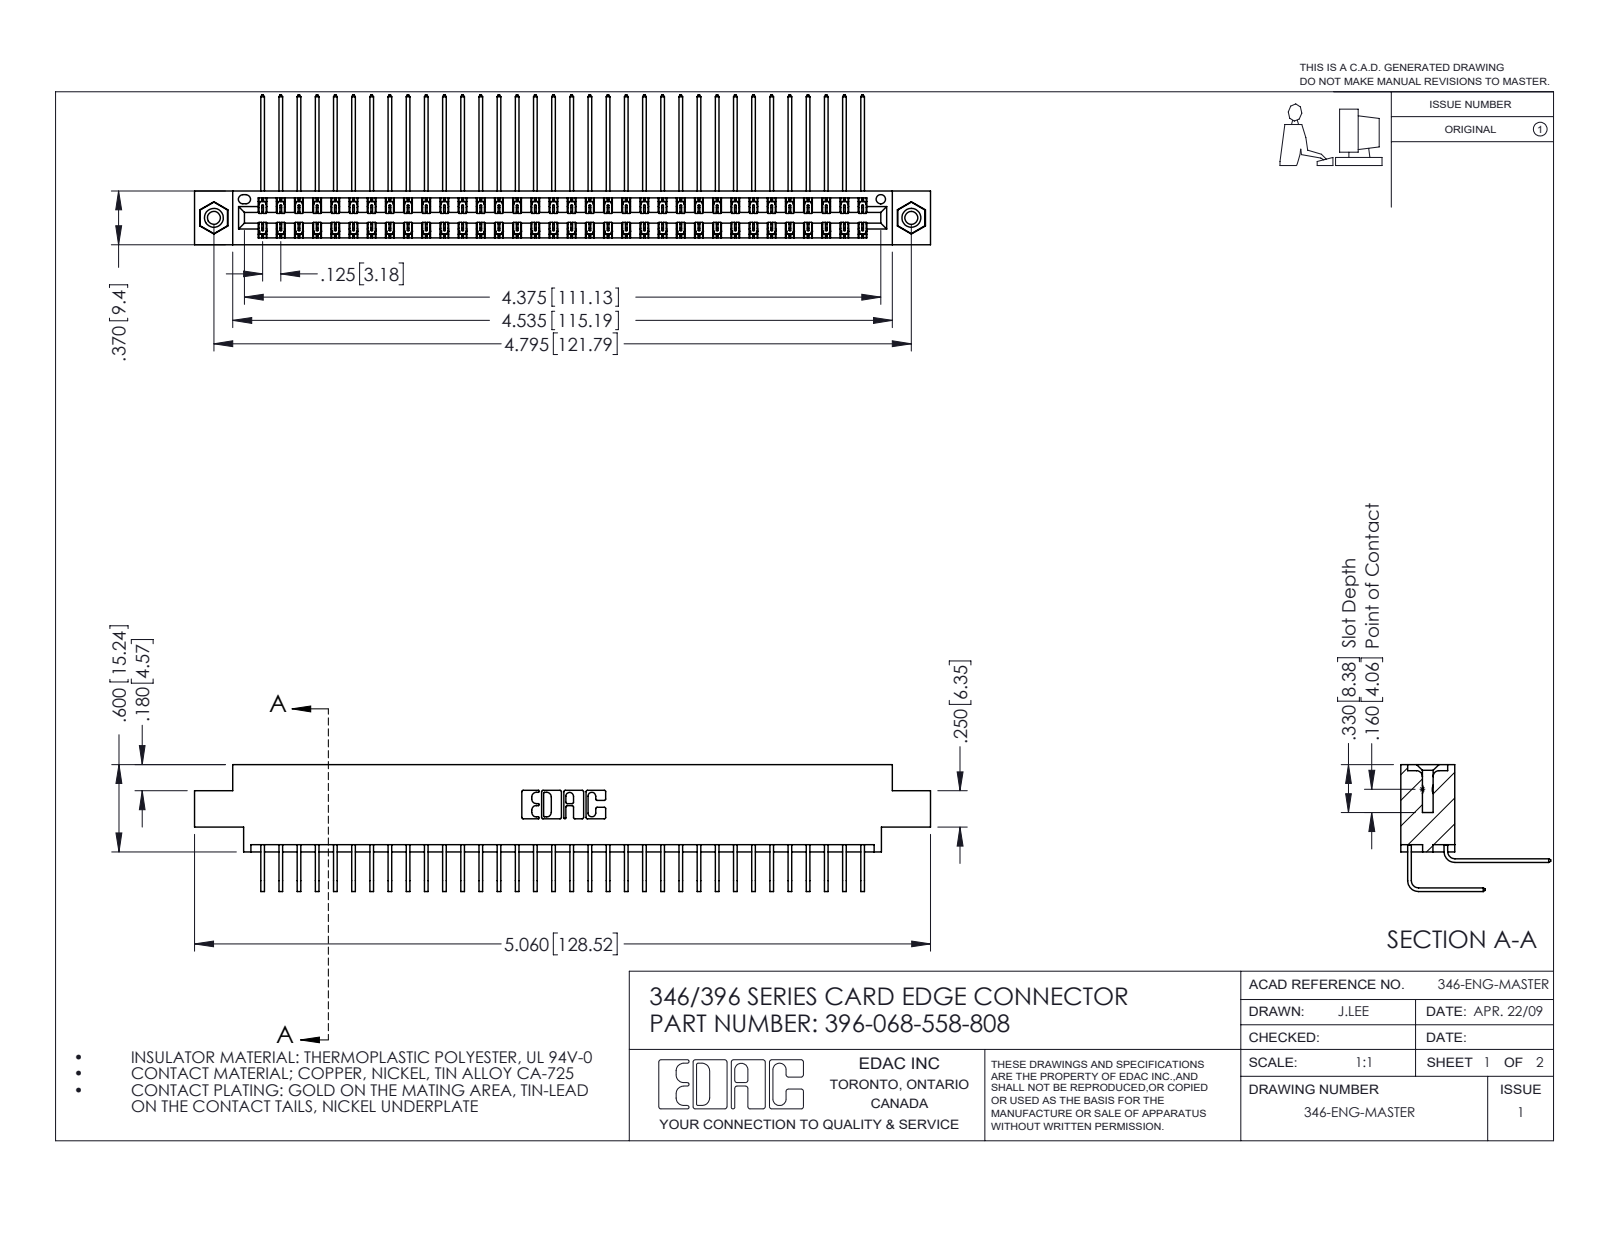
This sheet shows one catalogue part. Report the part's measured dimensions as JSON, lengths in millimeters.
{"part_name": "345-292-001_558 Tail - 2; 396-068-558-808; 345-292-001_558 559 Tail - 1; 345-250-001_345-250-003-102 (+1 more)", "step_written_by": "SolidWorks 2016 (CONFIG_CONTROL_DESIGN)", "units": "millimeters", "bodies": {"solids": 71, "faces": 3858, "planar": 2628, "cylindrical": 1214, "other": 16}, "overall_size": [128.5, 26.2, 22.2], "volume_mm3": 12700, "surface_area_mm2": 19410, "round_holes": [[2.3, 2], [3.2, 2], [4, 2], [1.6, 1]], "round_bosses_or_shafts": [[3.9, 2]], "partial_cylinders_radius": [[0.2, 102], [0.3, 22], [0.2, 6], [0.8, 6], [0.7, 3], [0.4, 2], [0.6, 2], [0.6, 2]], "face_to_face_distances": [8.2, 1.2, 0.6, 9.4, 6.4, 7.6, 1.8, 7, 5.6, 3.8], "hole_center_spacings": [6.2, 116.5, 121.8]}
